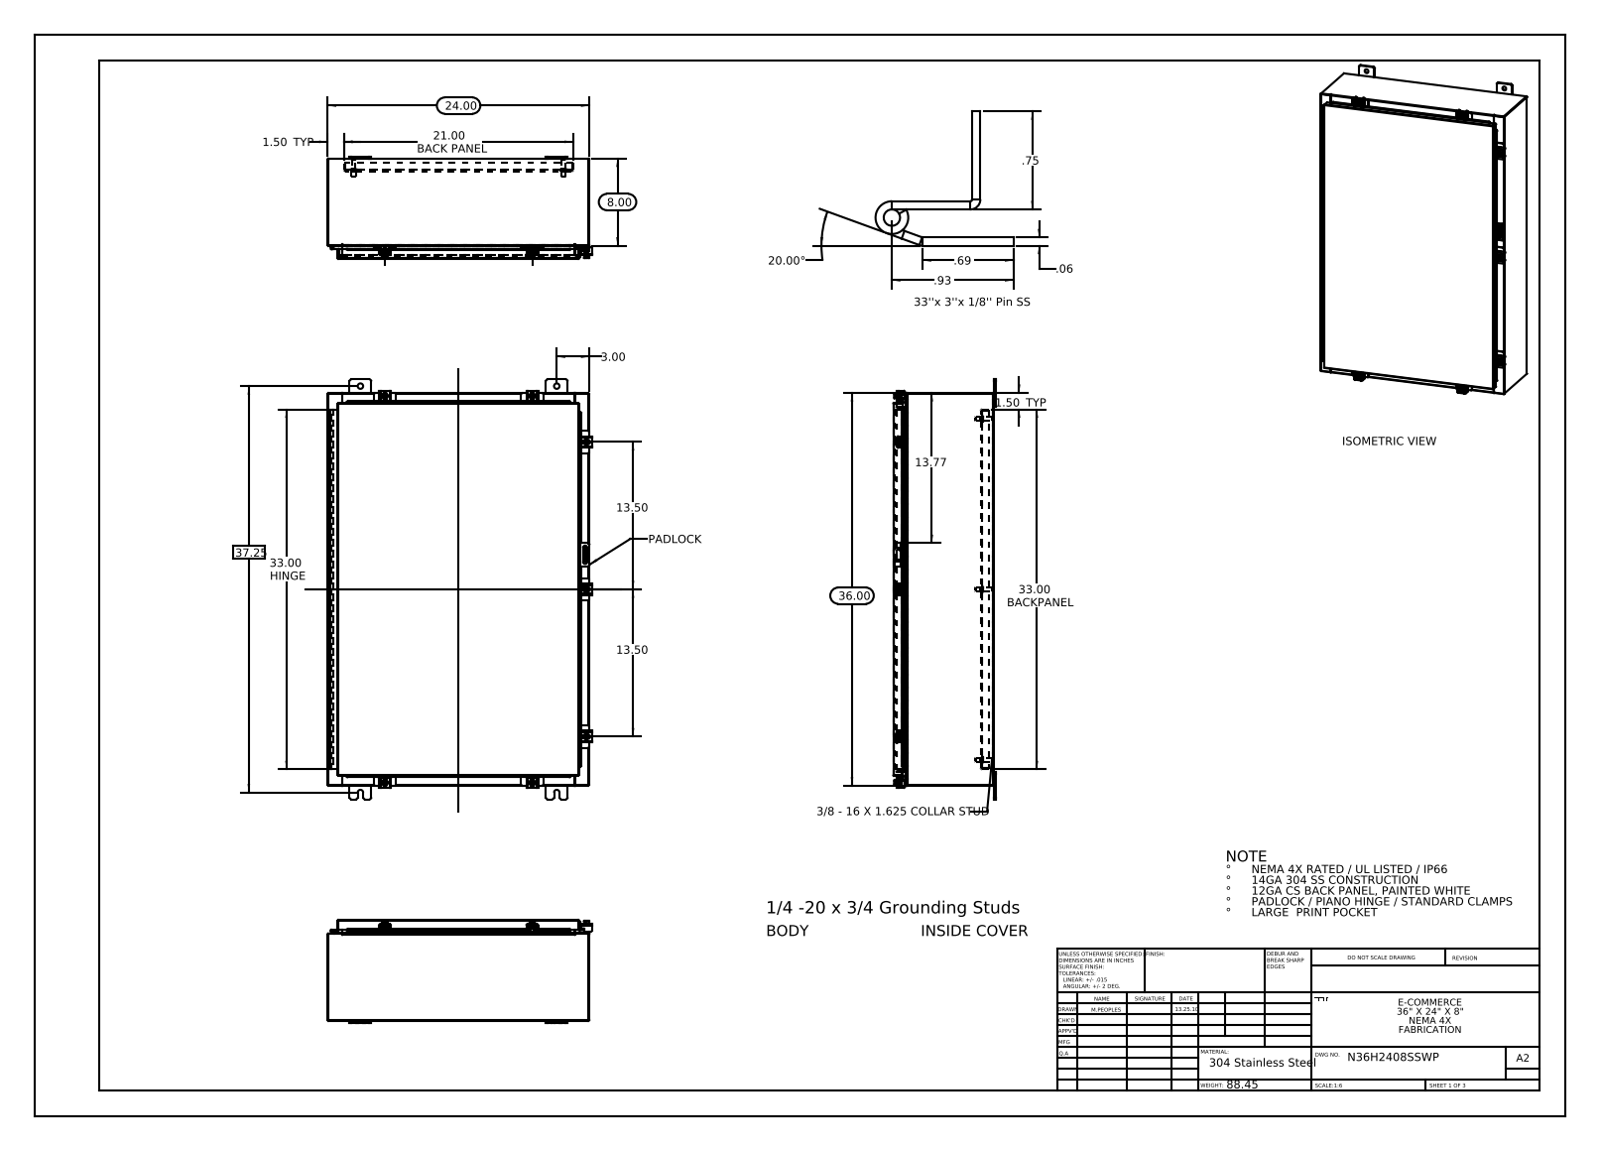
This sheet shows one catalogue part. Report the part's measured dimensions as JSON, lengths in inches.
{"part_name": "N36H2408SSWP Hinge Cover Side; N36H2408SSWP Body; N36H2408SSWP Hinge Enclosure Side2; N36H2408SSWP Mounting Studs (+8 more)", "step_written_by": "SolidWorks 2013 (CONFIG_CONTROL_DESIGN)", "units": "inches", "bodies": {"solids": 54, "faces": 2184, "planar": 1138, "cylindrical": 922, "other": 124}, "overall_size": [38.5, 24.211, 9.389], "volume_in3": 310.6, "surface_area_in2": 7747, "round_holes": [[0.5, 10], [0.213, 7], [0.26, 7], [0.125, 2], [0.125, 1]], "round_bosses_or_shafts": [[0.25, 8], [0.5, 7], [0.399, 7], [0.625, 6], [0.375, 6], [0.33, 6]], "partial_cylinders_radius": [[0.06, 34], [0.013, 27], [0.19, 24], [0.088, 21], [0.12, 14], [0.141, 14], [0.05, 11], [0.08, 10]], "face_to_face_distances": [0.075, 9.126, 9.201, 9.051, 0.104, 1, 1.075, 8.051, 8.126, 1.179], "hole_center_spacings": [13.5, 15.625, 17.957, 24.793, 33.474, 37.154, 19.25, 1.858]}
